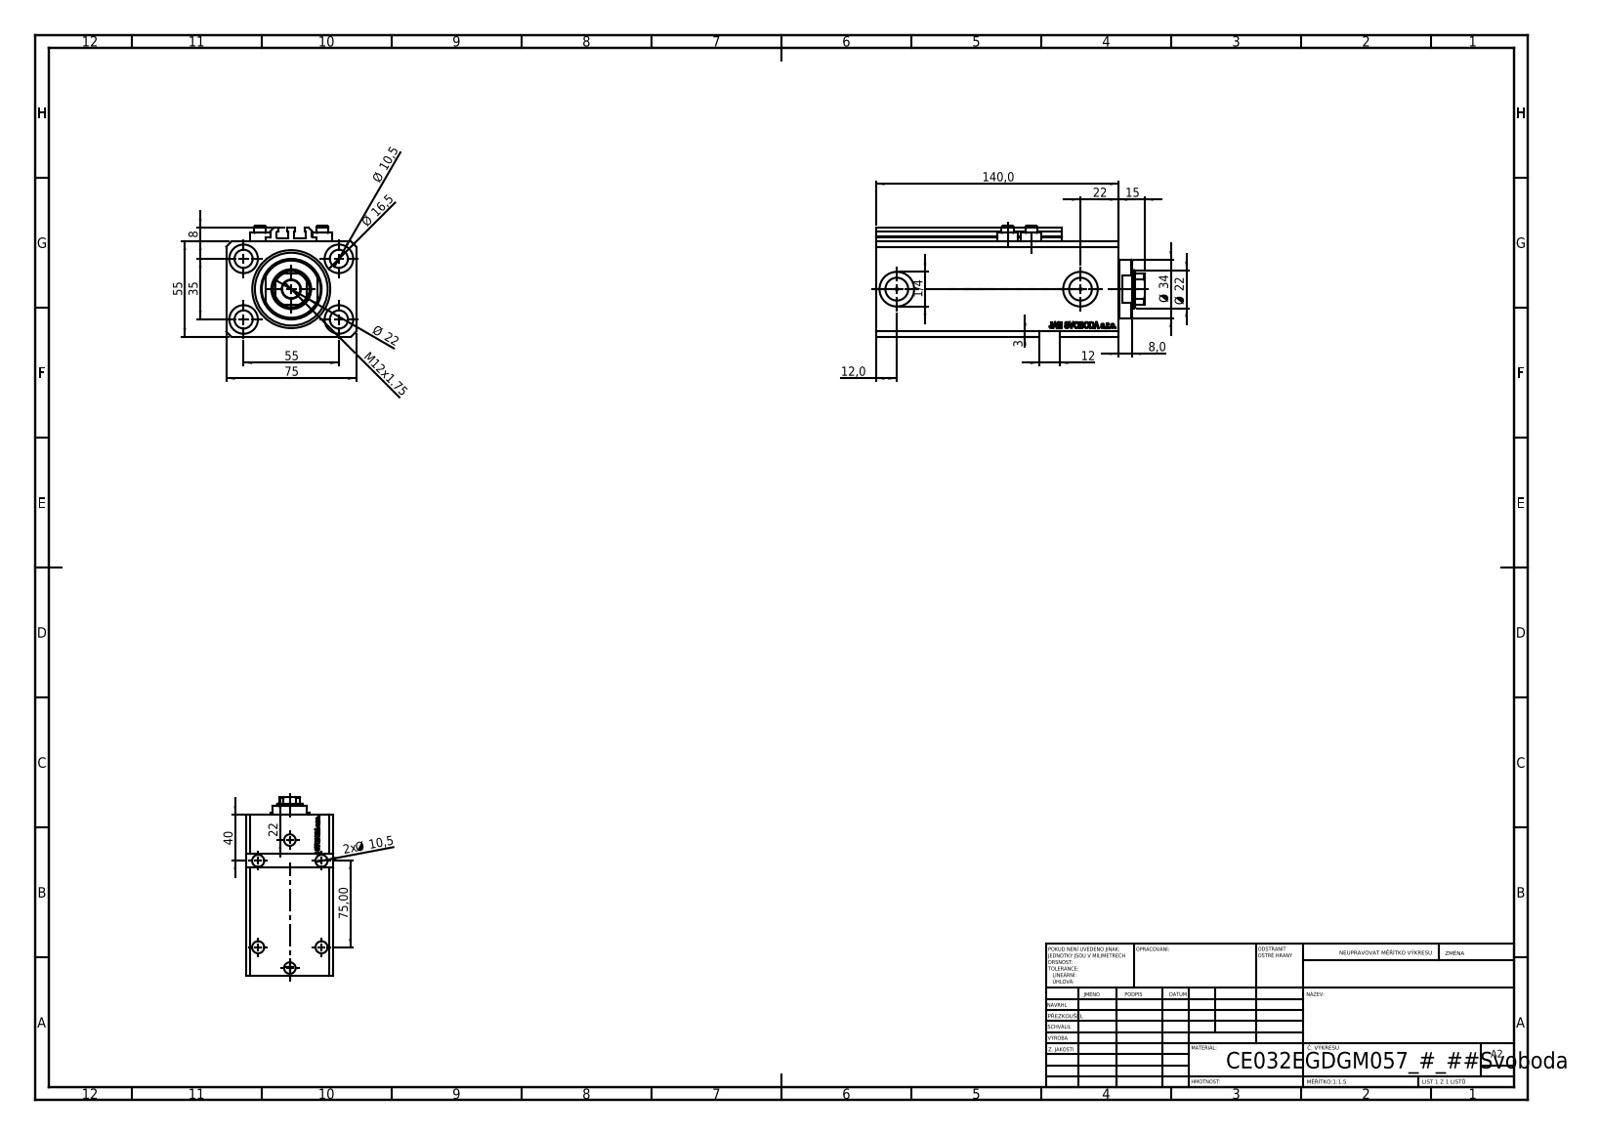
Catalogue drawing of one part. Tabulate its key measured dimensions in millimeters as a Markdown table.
| quantity | value |
| --- | --- |
| part name | V250CE_E_Body; ALLEN BOLT V250CE; V250CE_VC_E; V250CE_C_VCP |
| STEP written by | SolidWorks 2019 (CONFIG_CONTROL_DESIGN) |
| units | millimeters |
| bodies | 8 solids, 1100 faces (518 planar, 158 cylindrical, 424 other) |
| overall size | 155 × 75 × 64 |
| volume | 481 599 mm³ |
| surface area | 116 451 mm² |
| round holes (diameter × count) | 10.5 × 9, 1.25 × 4, 4 × 4, 16.5 × 4, 10 × 2, 13.16 × 2, 20 × 2, 22 × 1, 32 × 1, 45 × 1 |
| round bosses / shafts (diameter × count) | 11.6 × 4, 7 × 4, 34 × 1 |
| partial cylindrical surfaces (radius × count) | 0.2 × 10, 10.5 × 1 |
| main face-to-face distances | 55, 75, 15, 9.9, 140, 125, 3, 57, 115.1, 130.1 |
| hole center spacings | 32.6, 32.87, 55, 96.98, 13.6, 14.09, 25.81, 32.58 |
